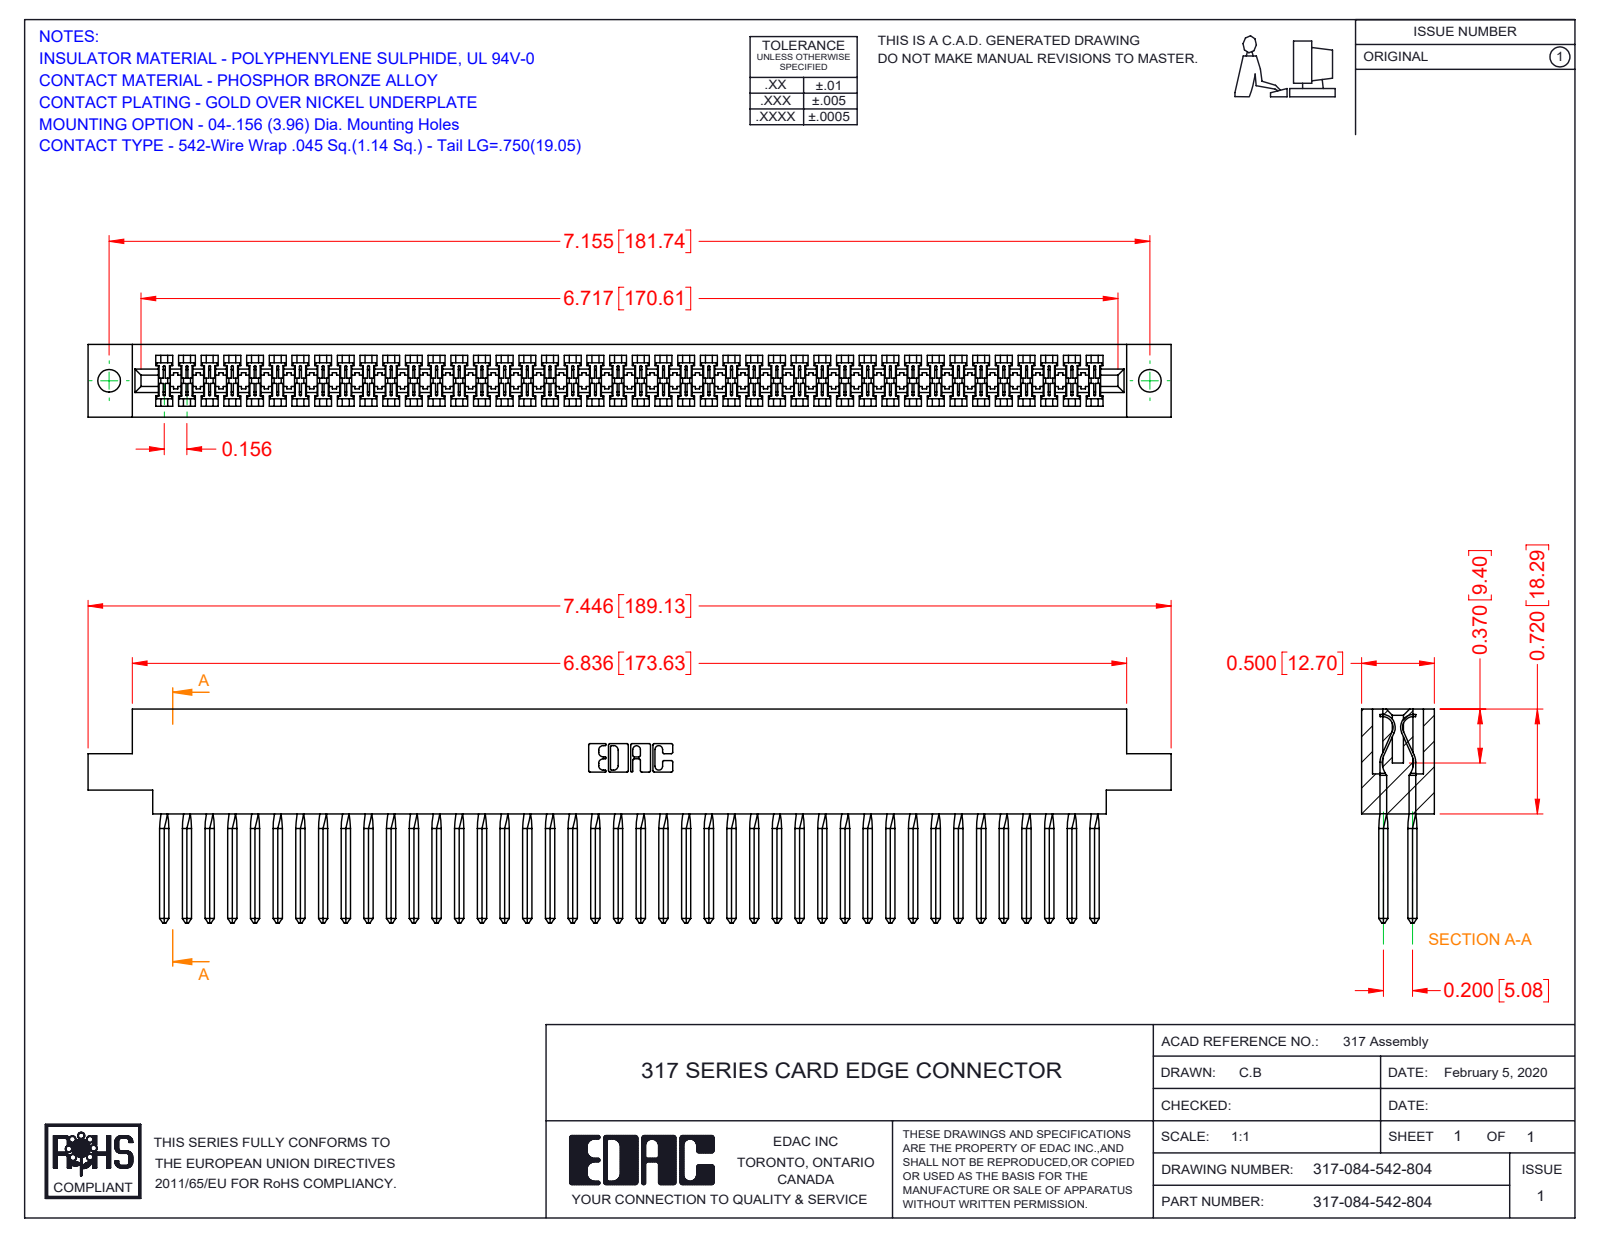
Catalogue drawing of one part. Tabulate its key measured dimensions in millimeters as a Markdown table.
| quantity | value |
| --- | --- |
| part name | 317-084-542-804; 317 Part_.156 Dia - TH; 317-290-003_542 |
| STEP written by | SolidWorks 2016 (CONFIG_CONTROL_DESIGN) |
| units | millimeters |
| bodies | 85 solids, 4890 faces (3922 planar, 632 cylindrical, 336 other) |
| overall size | 189.1 × 37.3 × 12.7 |
| volume | 30 870 mm³ |
| surface area | 42 760 mm² |
| round holes (diameter × count) | 4 × 2 |
| partial cylindrical surfaces (radius × count) | 0.2 × 168, 0.3 × 22, 0.2 × 6, 0.8 × 6, 0.7 × 3, 1.9 × 2, 2.3 × 2, 2.5 × 2 |
| main face-to-face distances | 12.7, 1.9, 10.8, 8.9, 5.1, 1.2, 3.3, 9.4, 1.3, 7.5 |
| hole center spacings | 181.7 |
